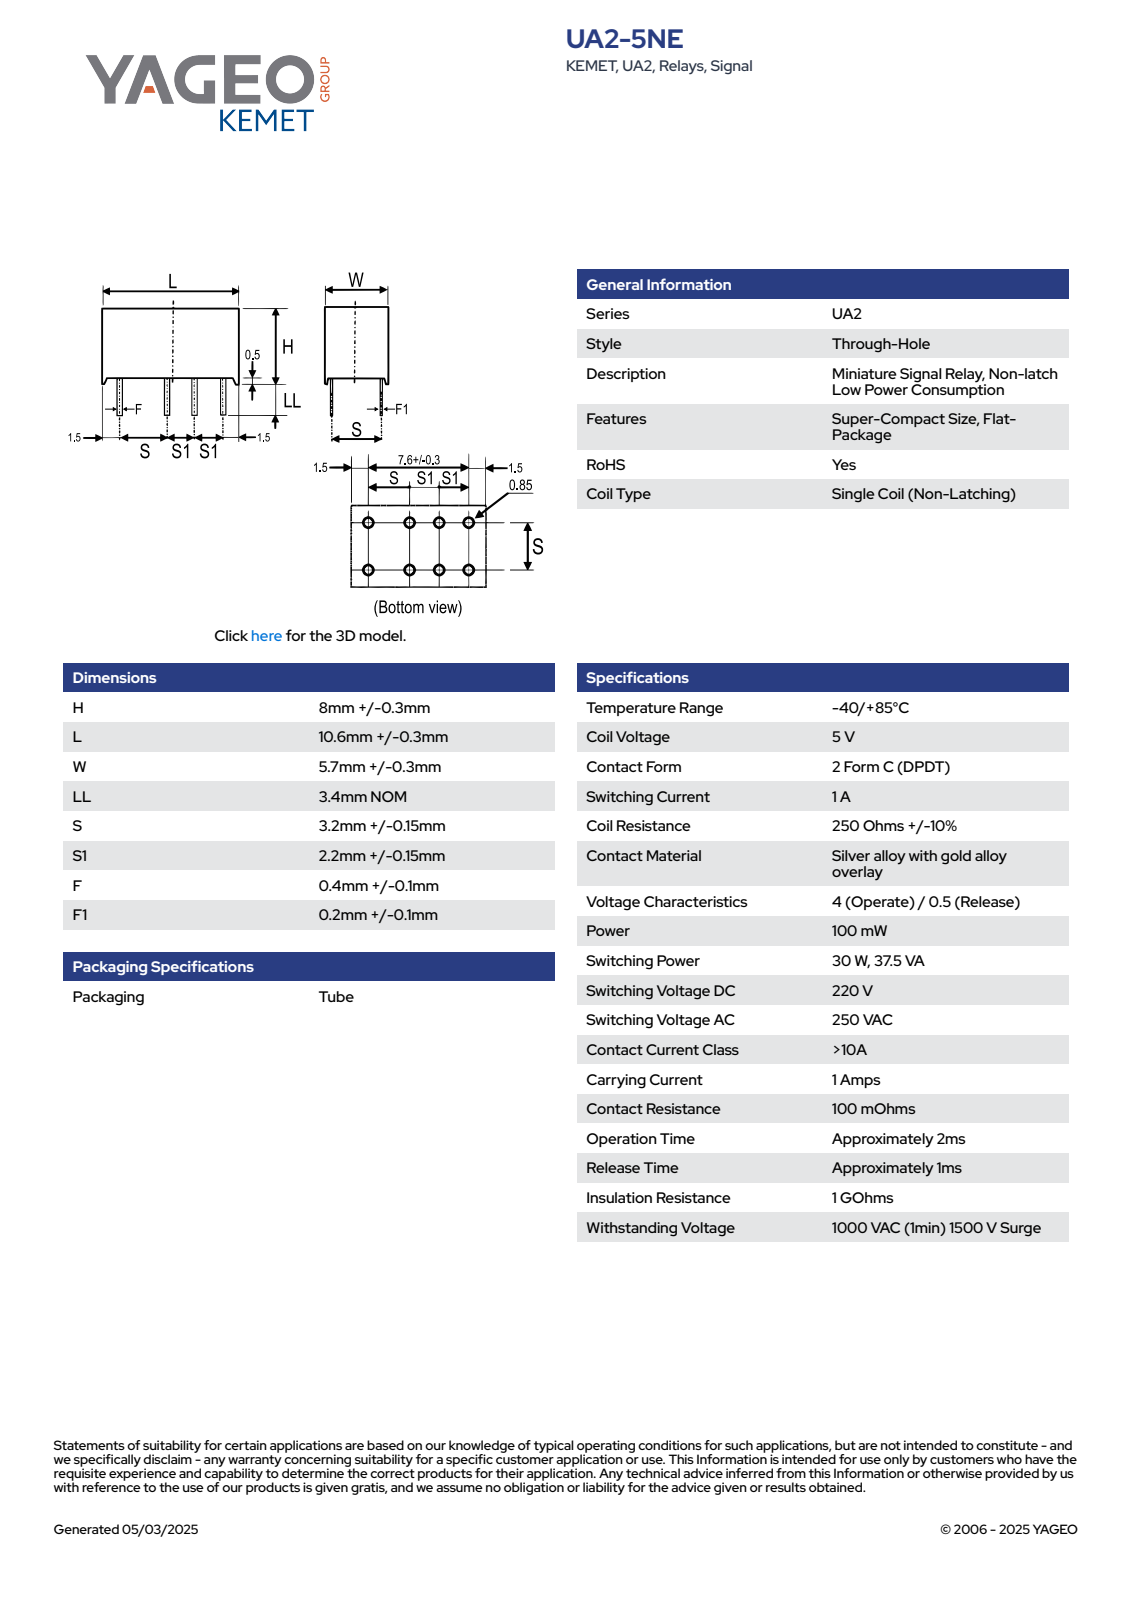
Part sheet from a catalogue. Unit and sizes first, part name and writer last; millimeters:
Units: millimetres
Overall size (bounding box): 12 × 10.9 × 6
Main face-to-face distances: 6, 7.8, 10.9, 3.2, 1.55, 1.25, 4.75, 4.45, 0.5, 2.2
Volume: 515 mm³ · Surface area: 451 mm²
Bodies: 1 solid, 112 faces (112 planar, 0 cylindrical, 0 other)
Part name (STEP PRODUCT): IR_TUA2_L10.9W6H8.3
STEP written by: SolidWorks 2014 (AUTOMOTIVE_DESIGN)
